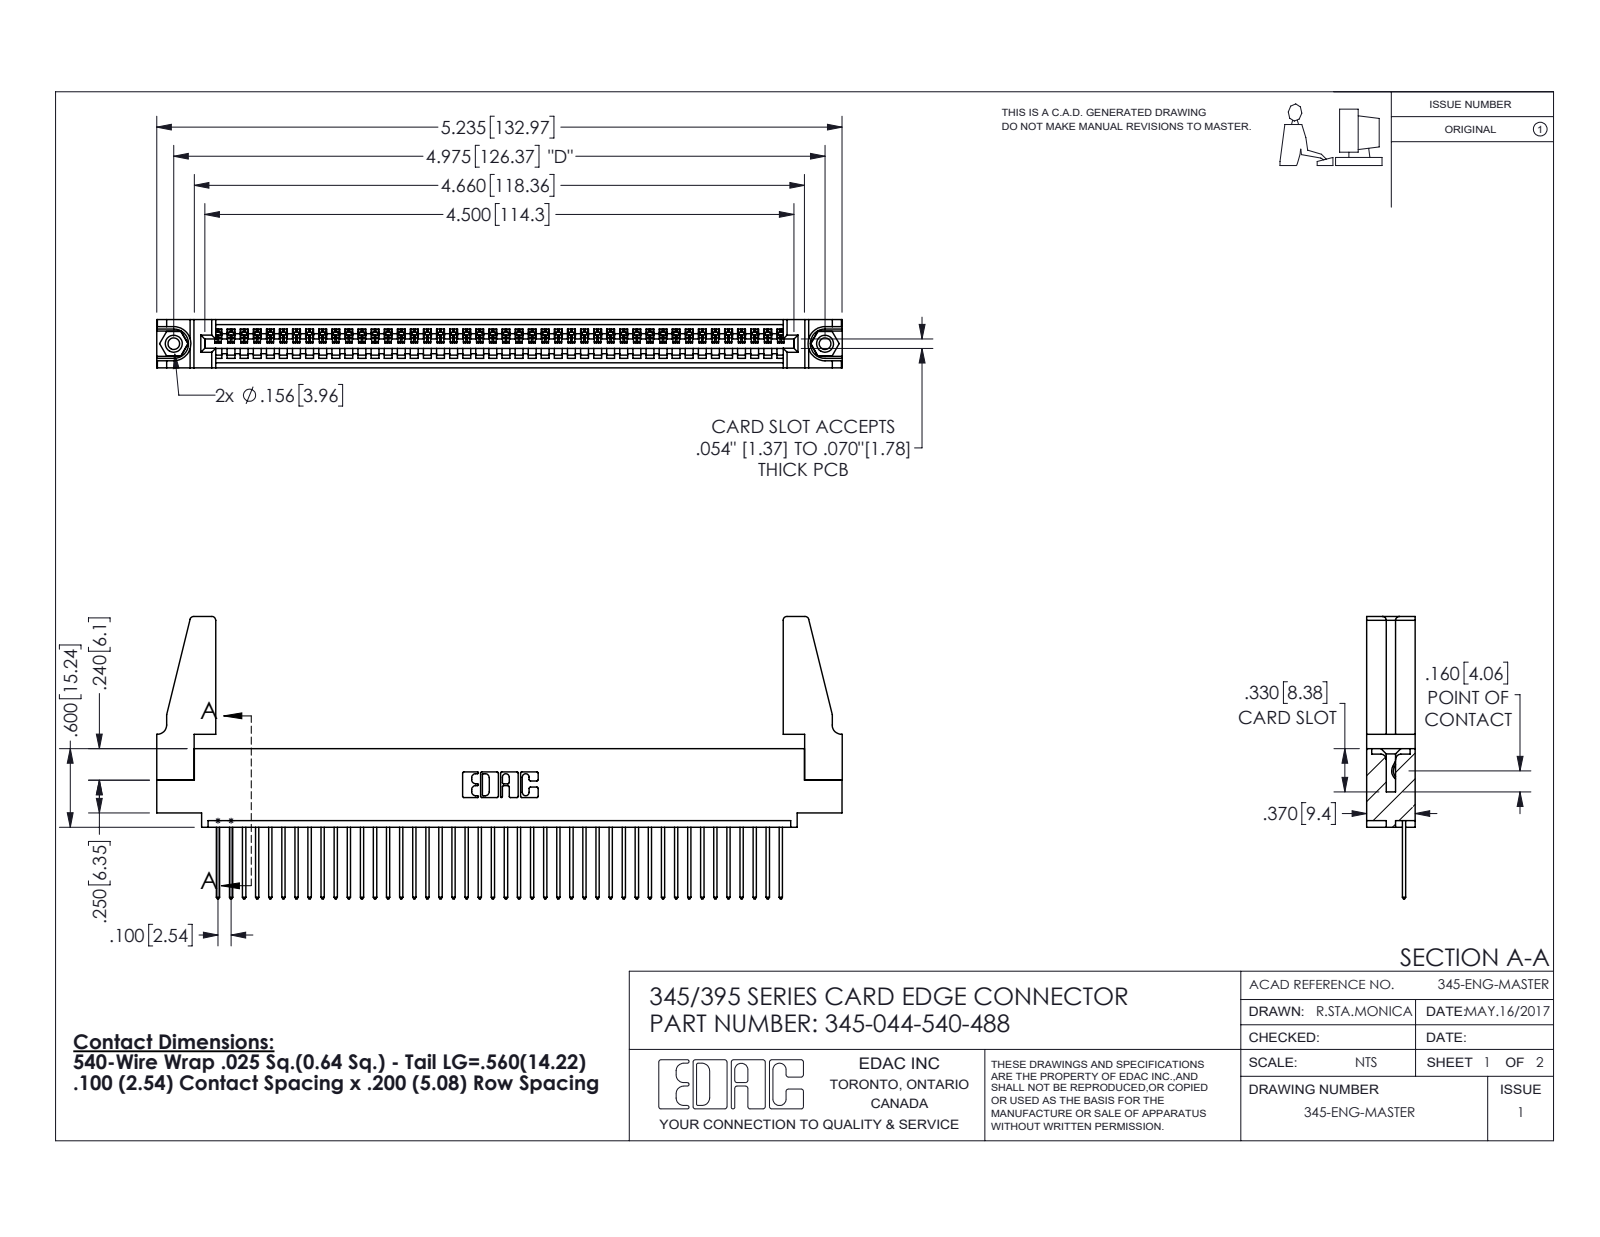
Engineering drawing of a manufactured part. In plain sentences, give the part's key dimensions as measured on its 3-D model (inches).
The part is named "345 Part_0.110 Offset - 0.156 Dia-TH; 345-044-540-488; 345-250-001_345-250-001-102; 345-292-001_345-293-140 (+1 more)". Its 3-D file was written by "SolidWorks 2016 (CONFIG_CONTROL_DESIGN)". It is 49 solids with 2806 faces: 1916 planar, 874 cylindrical and 16 other. Overall it measures 5.236 by 2.157 by 0.37 inches. Its volume is 0.969 cubic inches and its surface area 31.71 square inches. Round holes: 2 of diameter 0.089, 2 of diameter 0.125, 2 of diameter 0.156, 1 of diameter 0.064. Round bosses or shafts: 2 of diameter 0.155. Partial cylindrical surfaces (rounded edges, fillets, slot ends): 88 of radius 0.006, 88 of radius 0.01, 22 of radius 0.01, 8 of radius 0.03, 6 of radius 0.007, 6 of radius 0.031, 3 of radius 0.026, 2 of radius 0.031. The main face-to-face distances are 0.072, 0.298, 0.37, 0.098, 0.272, 0.025, 0.2, 0.225, 0.149, 0.072. The hole center spacings are 0.27, 4.739, 4.975.
